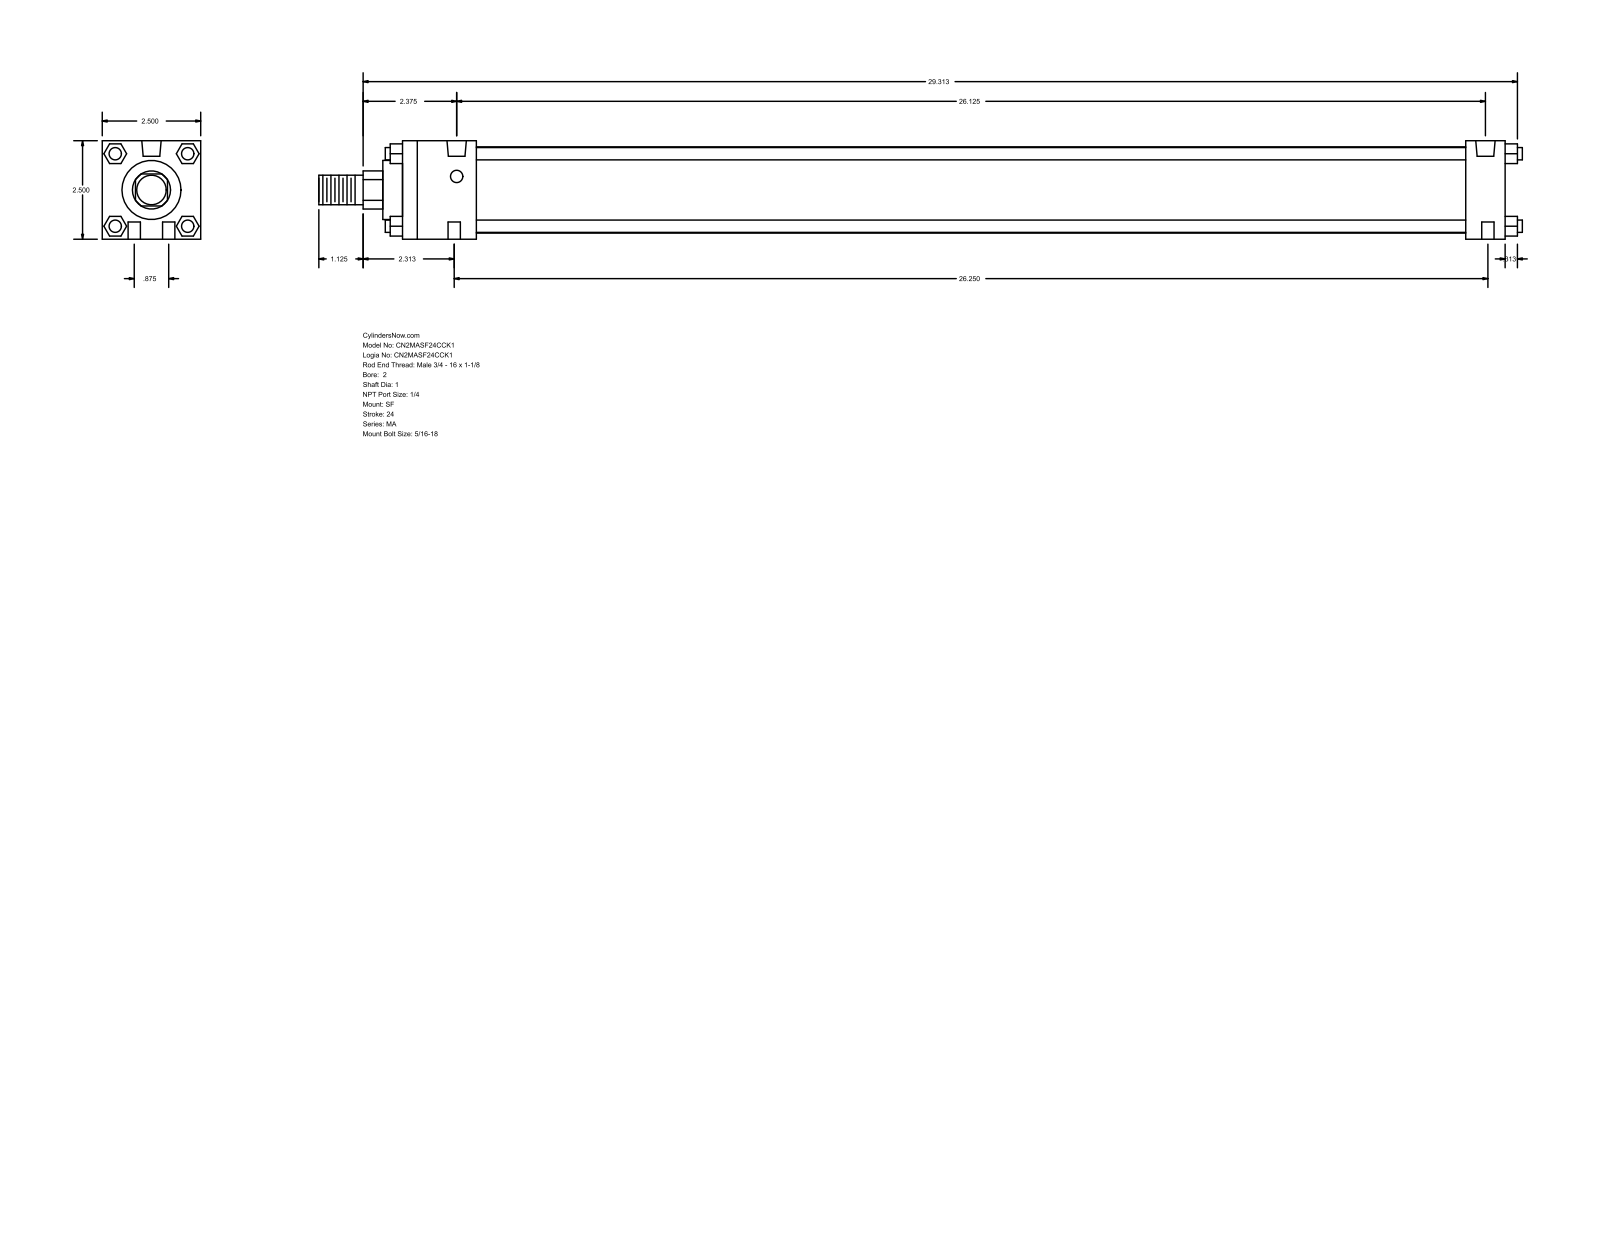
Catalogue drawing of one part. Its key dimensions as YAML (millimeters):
part_name: "MA_SF__0200_1"
step_written_by: "GSSL Pune (CONFIG_CONTROL_DESIGN)"
units: millimeters
bodies: {solids: 0, faces: 124, planar: 94, cylindrical: 30, other: 0}
overall_size: [776.29, 63.5, 63.5]
round_holes:
  - {diameter: 7.94, count: 6}
  - {diameter: 12.49, count: 2}
round_bosses_or_shafts:
  - {diameter: 7.94, count: 4}
  - {diameter: 55.63, count: 1}
  - {diameter: 38.1, count: 1}
  - {diameter: 25.4, count: 1}
  - {diameter: 19.05, count: 1}
partial_cylinders:
  - {radius: 12.29, count: 1}
face_to_face_distances: [63.5, 711.2, 12.7, 25.4, 685.8, 47.63, 638.17, 663.57, 40.47, 23.37]
hole_center_spacings: [11.22, 665.25, 22.22, 663.57, 666.75, 667.12]
